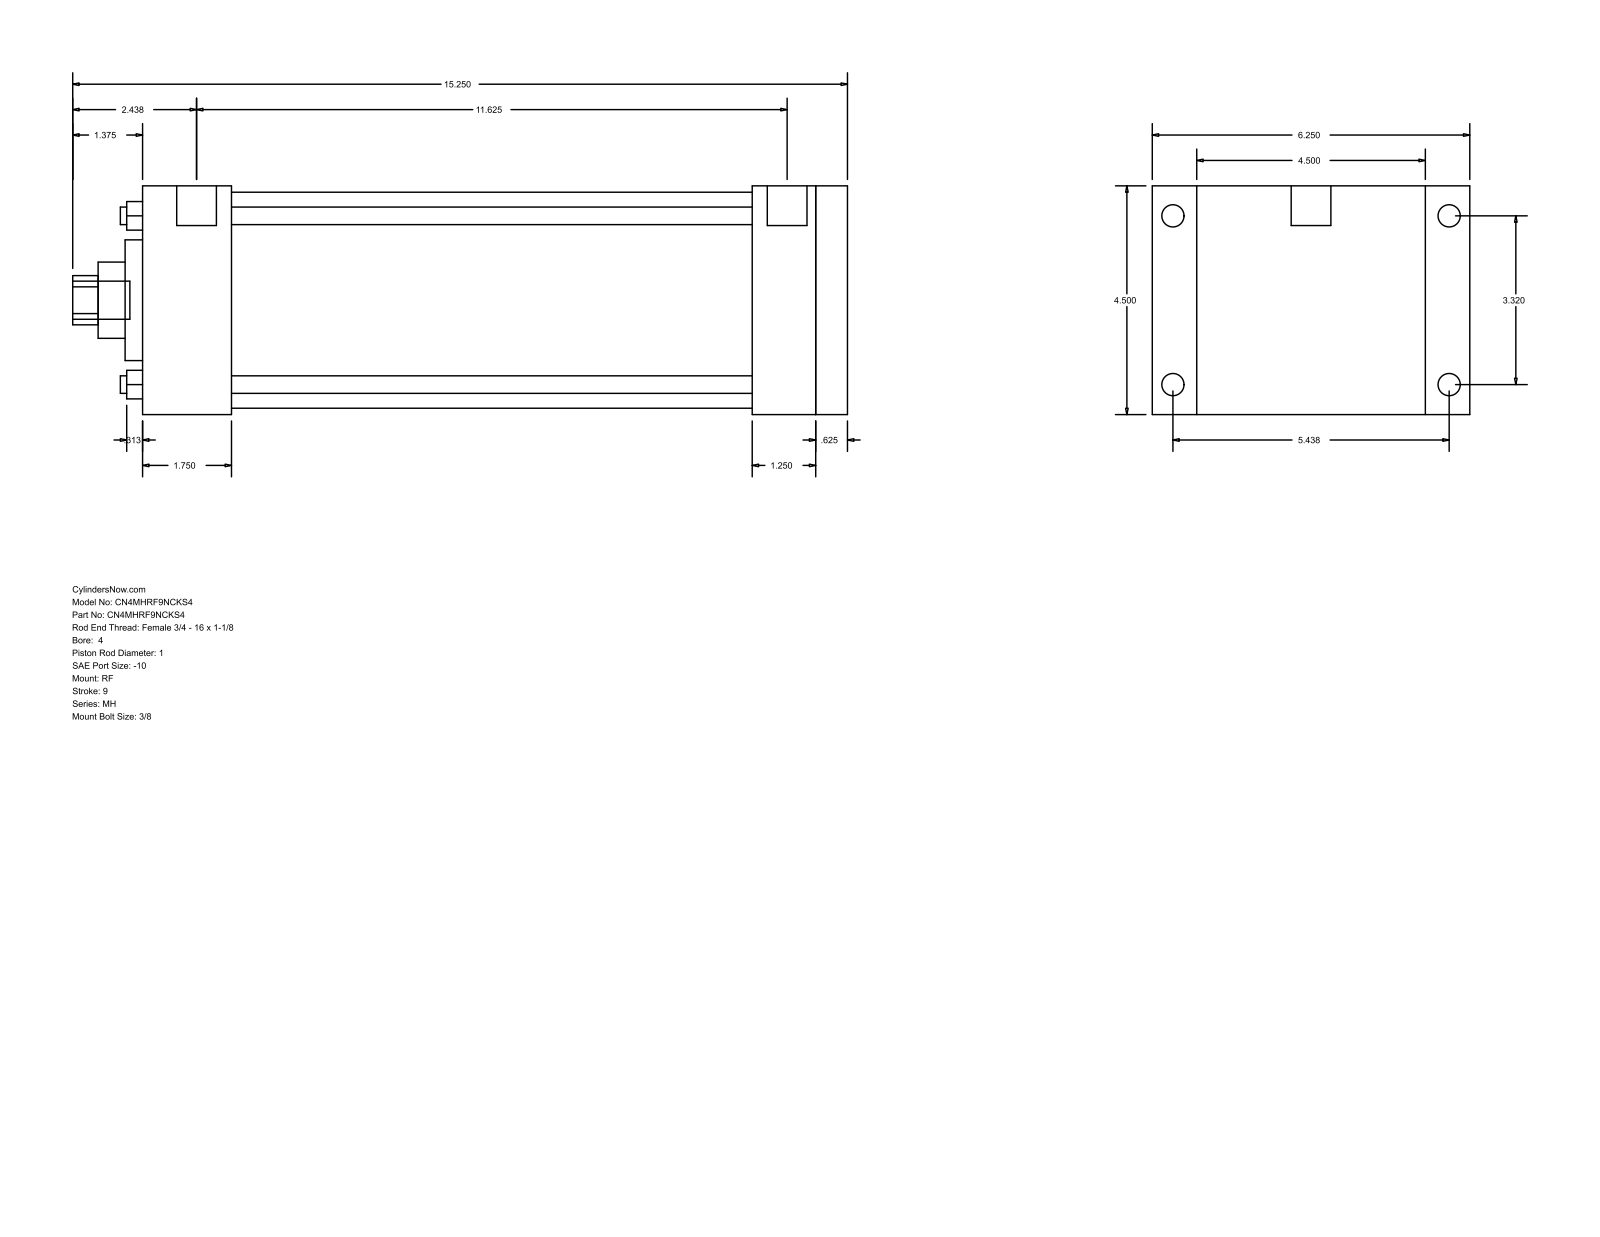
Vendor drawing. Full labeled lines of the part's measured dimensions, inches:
Part name (STEP PRODUCT): MH_RF__0400_1
STEP written by: GSSL Pune (CONFIG_CONTROL_DESIGN)
Units: inches
Bodies: 0 solids, 94 faces (65 planar, 29 cylindrical, 0 other)
Overall size (bounding box): 15.25 × 6.25 × 4.5
Round holes (diameter × count): ⌀0.345 ×4, ⌀1 ×1, ⌀1.5 ×1, ⌀2.375 ×1, ⌀4.25 ×1
Round bosses / shafts (diameter × count): ⌀0.438 ×4, ⌀0.344 ×4, ⌀0.781 ×2, ⌀0.75 ×1
Partial cylindrical surfaces — rounded edges, fillets, slot ends (radius × count): R0.484 ×1
Main face-to-face distances: 4.5, 13.875, 0.625, 13.25, 1.75, 11.5, 12.125, 12, 10.25, 1.25
Hole centre spacings: 2.347, 3.32, 4.695
